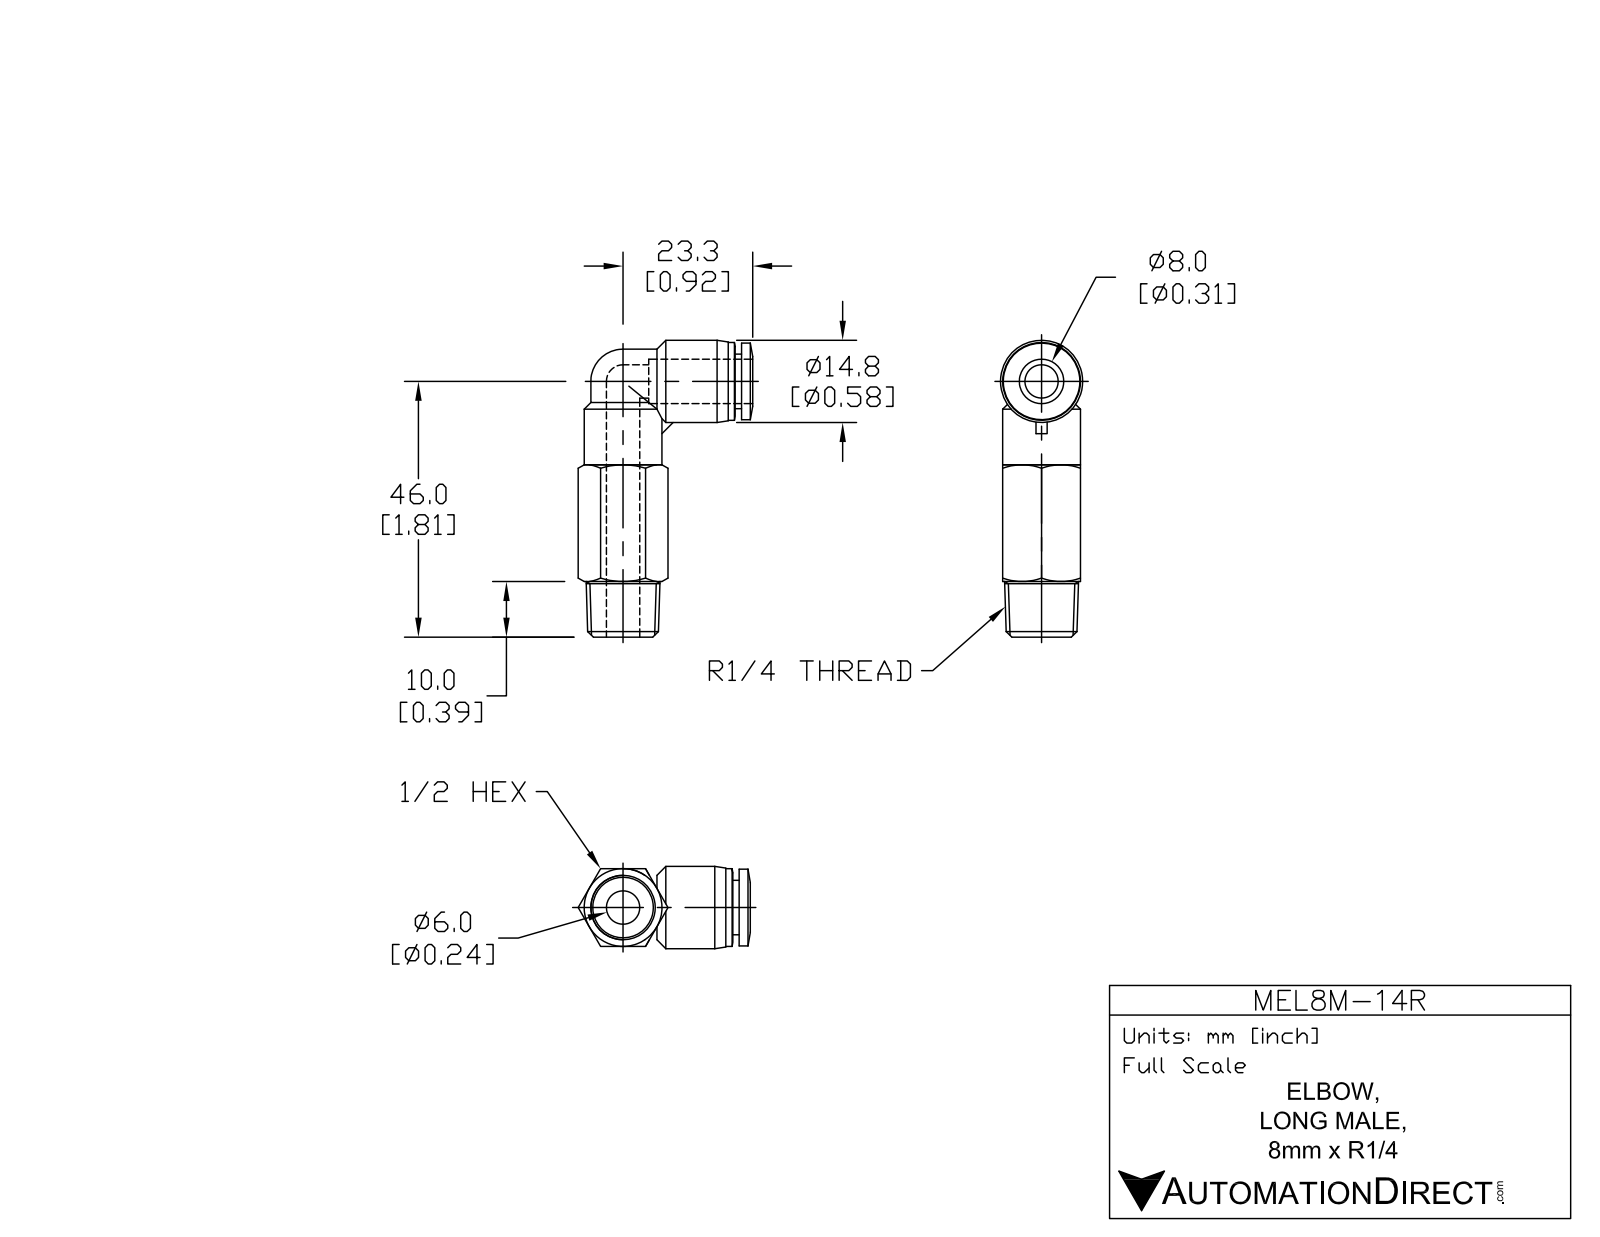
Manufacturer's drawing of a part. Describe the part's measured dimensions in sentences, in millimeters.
The part is named "MEL8M-14R". Its 3-D file was written by "SolidWorks 2015 (AUTOMOTIVE_DESIGN)". It is 1 solid with 68 faces: 16 planar, 19 cylindrical and 33 other. Overall it measures 53.4 by 31 by 14.8 millimeters. Its volume is 7 750 cubic millimeters and its surface area 4 801 square millimeters. Round holes: 2 of diameter 6, 1 of diameter 8.3. Round bosses or shafts: 2 of diameter 14, 1 of diameter 14.8, 1 of diameter 13.8, 1 of diameter 11.6, 1 of diameter 9.8. Partial cylindrical surfaces (rounded edges, fillets, slot ends): 1 of radius 5.8. The main face-to-face distances are 14, 1.1, 15.1, 16.3, 10, 2, 18.3, 3.1, 6, 8.
